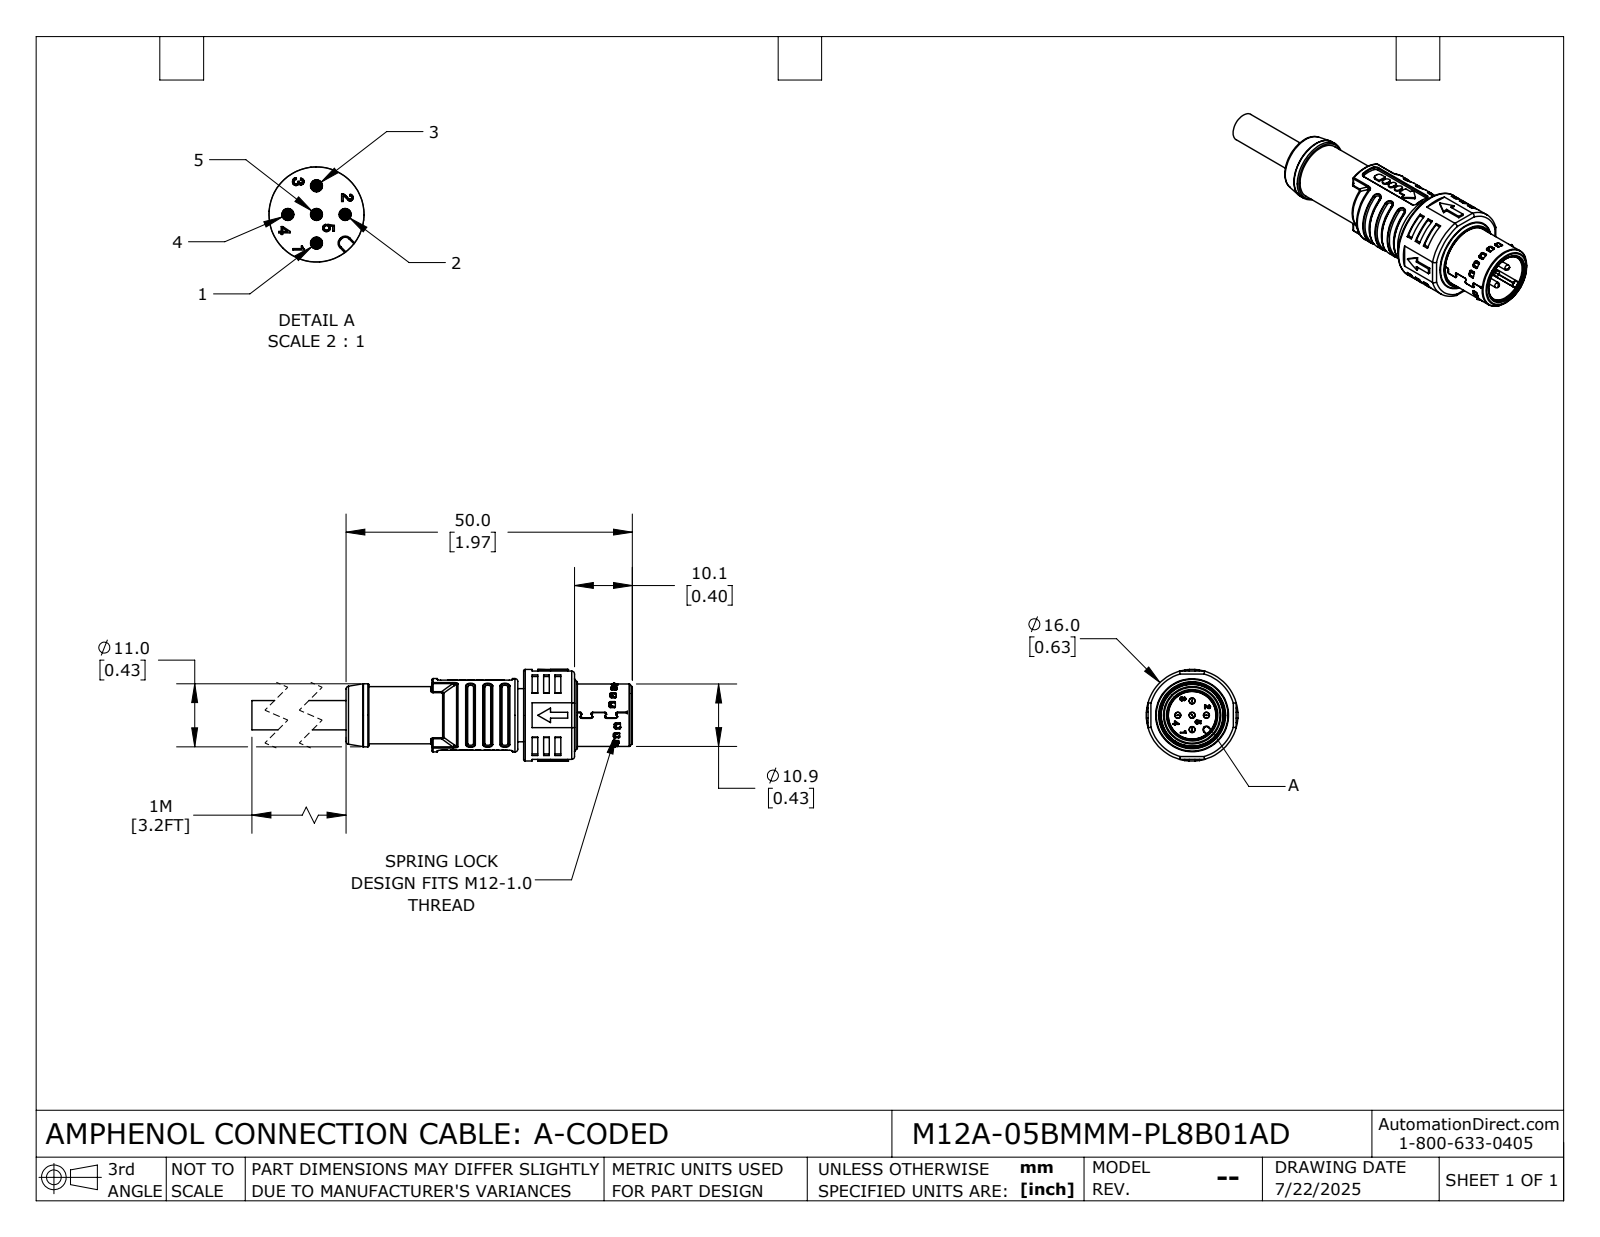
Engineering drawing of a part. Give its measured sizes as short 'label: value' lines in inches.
name: M12A-05BMMM-PL8B01AD
written by: SolidWorks 2024 (CONFIG_CONTROL_DESIGN)
unit: in
bodies: 1 solid, 2230 faces (1085 planar, 648 cylindrical, 497 other)
size: 2.559 × 0.63 × 0.63
volume: 0.31 in³; area: 8.658 in²
holes: 5× ⌀0.041, 1× ⌀0.327, 1× ⌀0.354, 1× ⌀0.4, 1× ⌀0.413, 1× ⌀0.429, 1× ⌀0.453, 1× ⌀0.465, 1× ⌀0.559
bosses: 5× ⌀0.039, 1× ⌀0.63, 1× ⌀0.555, 1× ⌀0.504, 1× ⌀0.488, 1× ⌀0.433, 1× ⌀0.411, 1× ⌀0.409
rounds: 114× R0.008, 66× R0.01, 64× R0.012, 44× R0.006, 38× R0.02, 12× R0.005, 11× R0.028, 10× R0.004
face distances: 0.039, 0.398, 0.35, 0.339, 0.098, 1.181, 0.059, 0.047, 1.28, 0.606
hole spacings: 0.098, 0.139, 0.197
